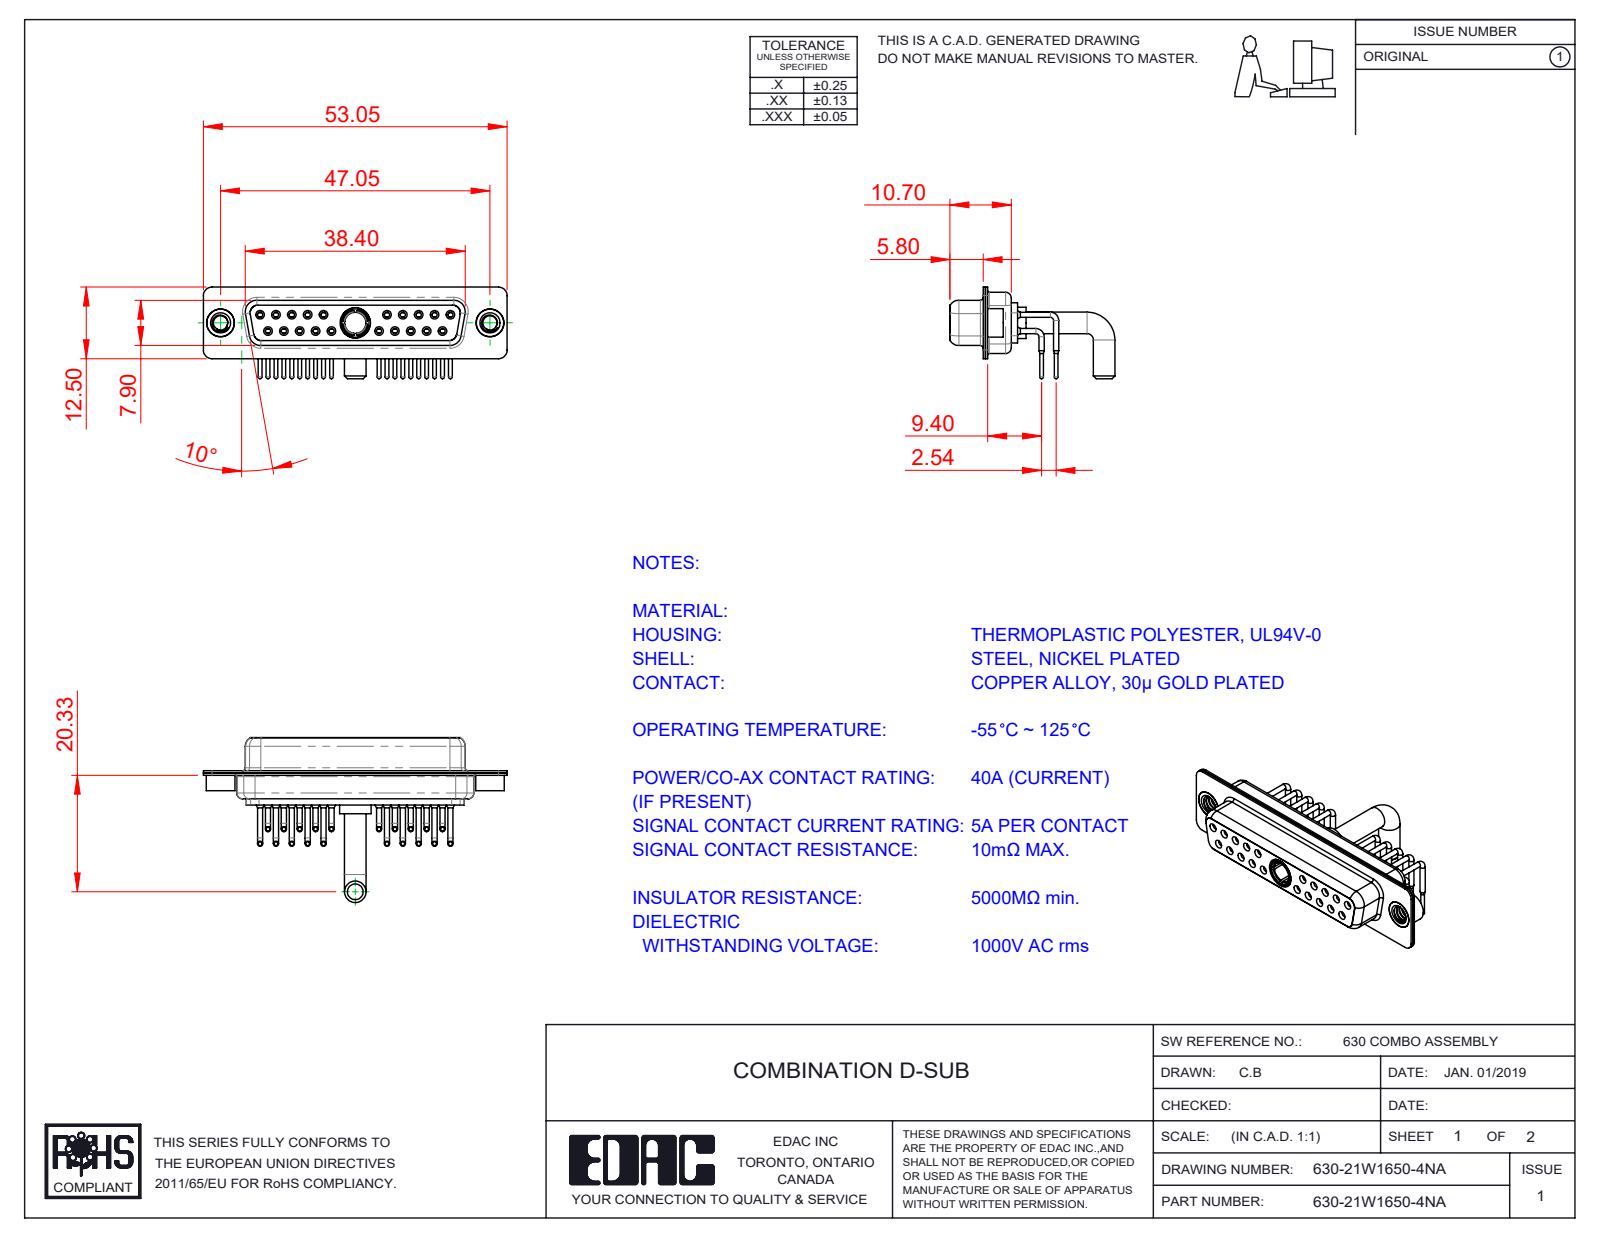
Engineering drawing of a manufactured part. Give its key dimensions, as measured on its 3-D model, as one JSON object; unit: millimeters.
{"part_name": "630Combo Contact Row 1; 630Combo Contact Row 2; 630Combo Shell Rear_25 Contacts; 630Combo Housing_21W1 (+4 more)", "step_written_by": "SolidWorks 2020 (CONFIG_CONTROL_DESIGN)", "units": "millimeters", "bodies": {"solids": 27, "faces": 1411, "planar": 396, "cylindrical": 620, "other": 395}, "overall_size": [53.05, 28.8, 16], "volume_mm3": 4171, "surface_area_mm2": 9482, "round_holes": [[0.9, 20], [1.1, 20], [1.5, 20], [2, 20], [1.6, 10], [1.7, 10], [4.85, 3], [2.5, 2], [4, 2], [4.05, 2], [3.7, 1], [5.3, 1]], "round_bosses_or_shafts": [[0.9, 20], [0.65, 20], [1.6, 10], [5, 2], [4.95, 2], [4.8, 2], [3.75, 2], [5.5, 1]], "partial_cylinders_radius": [[1.5, 16], [2, 12], [1.35, 8], [1.6, 8], [0.25, 4], [0.5, 4], [0.6, 4], [0.65, 4]], "face_to_face_distances": [0.4, 1.4, 0.45, 8.45, 1.8, 8.9, 6.2, 7.05, 1.85, 8.85], "hole_center_spacings": [3.16, 2.77, 5.54, 8.31, 5.04, 19.39, 20.97, 22.16]}
